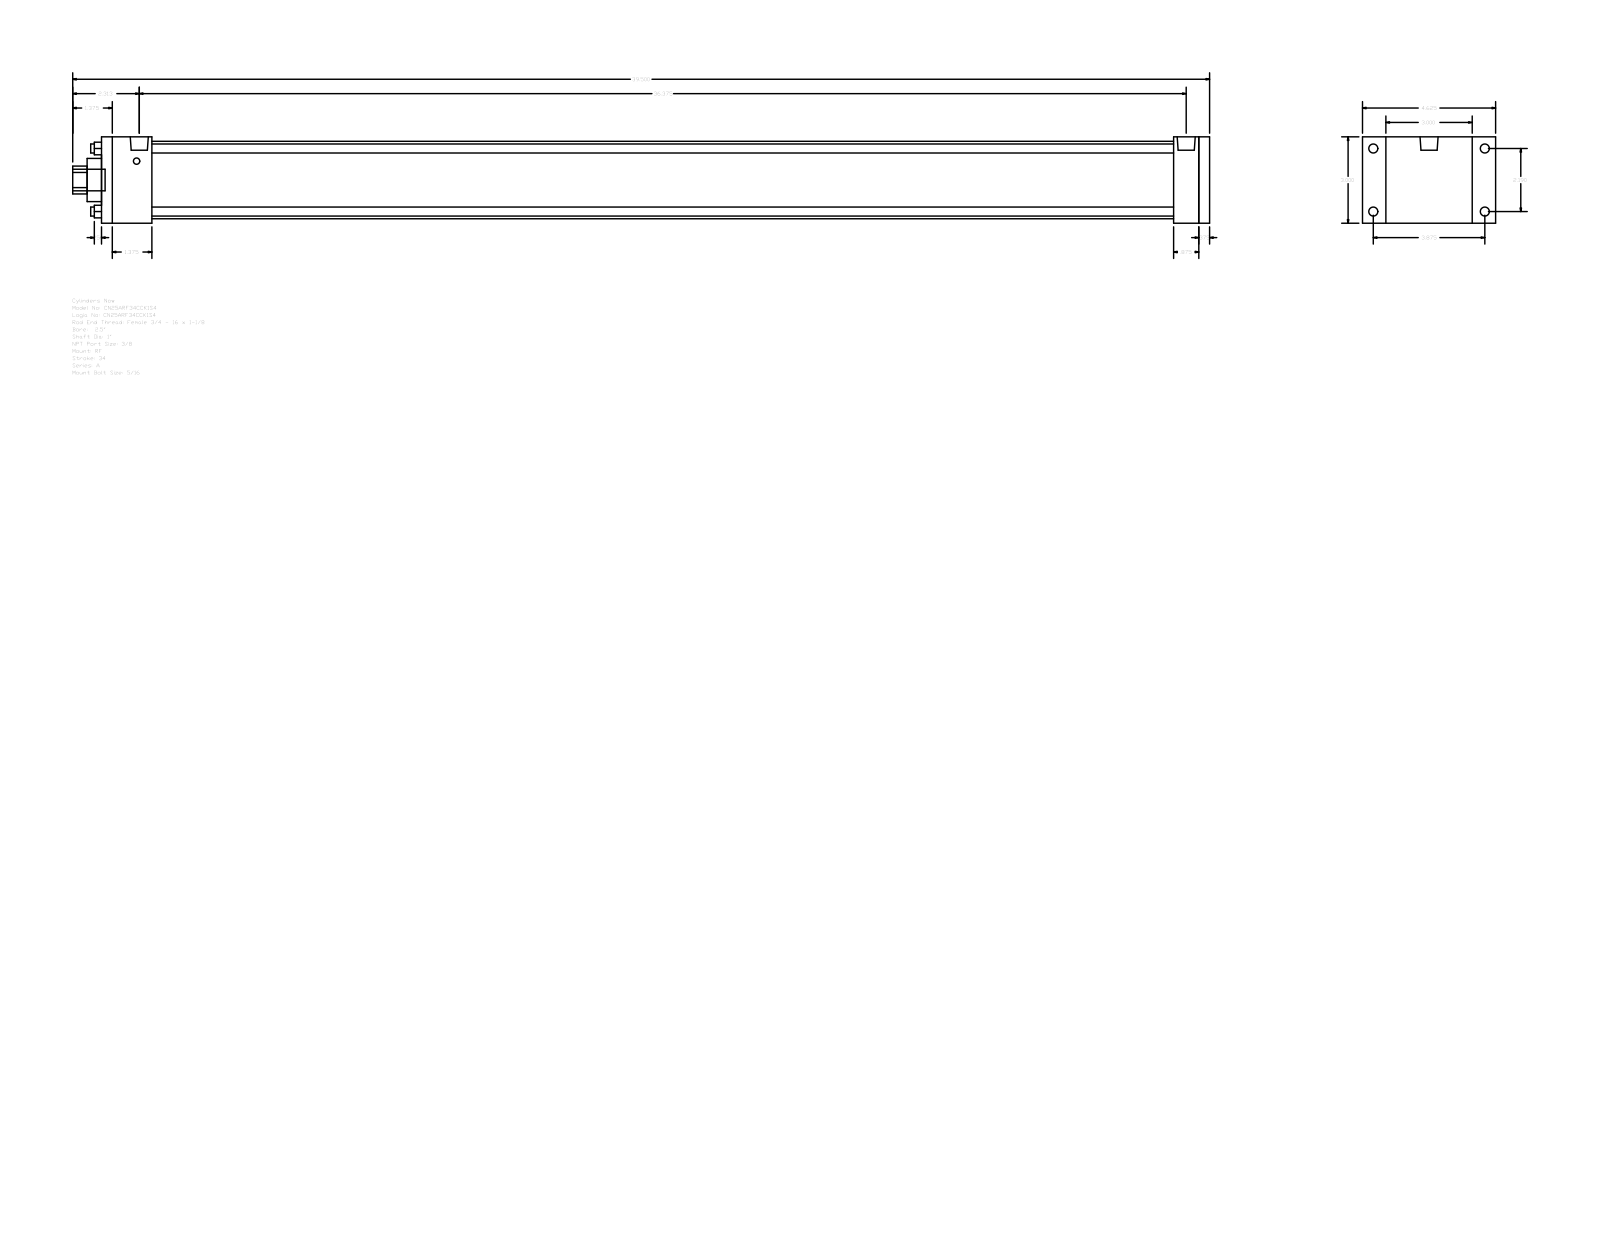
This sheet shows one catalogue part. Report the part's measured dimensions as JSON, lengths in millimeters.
{"part_name": "A_RF__0250_1", "step_written_by": "GSSL Pune (CONFIG_CONTROL_DESIGN)", "units": "millimeters", "bodies": {"solids": 0, "faces": 92, "planar": 64, "cylindrical": 28, "other": 0}, "overall_size": [1003.3, 117.47, 76.2], "round_holes": [[7.94, 4], [25.4, 1], [38.1, 1], [68.33, 1]], "round_bosses_or_shafts": [[7.94, 4], [5.56, 4], [15.93, 2], [19.05, 1]], "partial_cylinders_radius": [[12.29, 1]], "face_to_face_distances": [76.2, 977.9, 9.53, 968.37, 44.45, 946.15, 901.7, 923.92, 933.45, 22.22], "hole_center_spacings": [39.33, 55.62, 78.66]}
